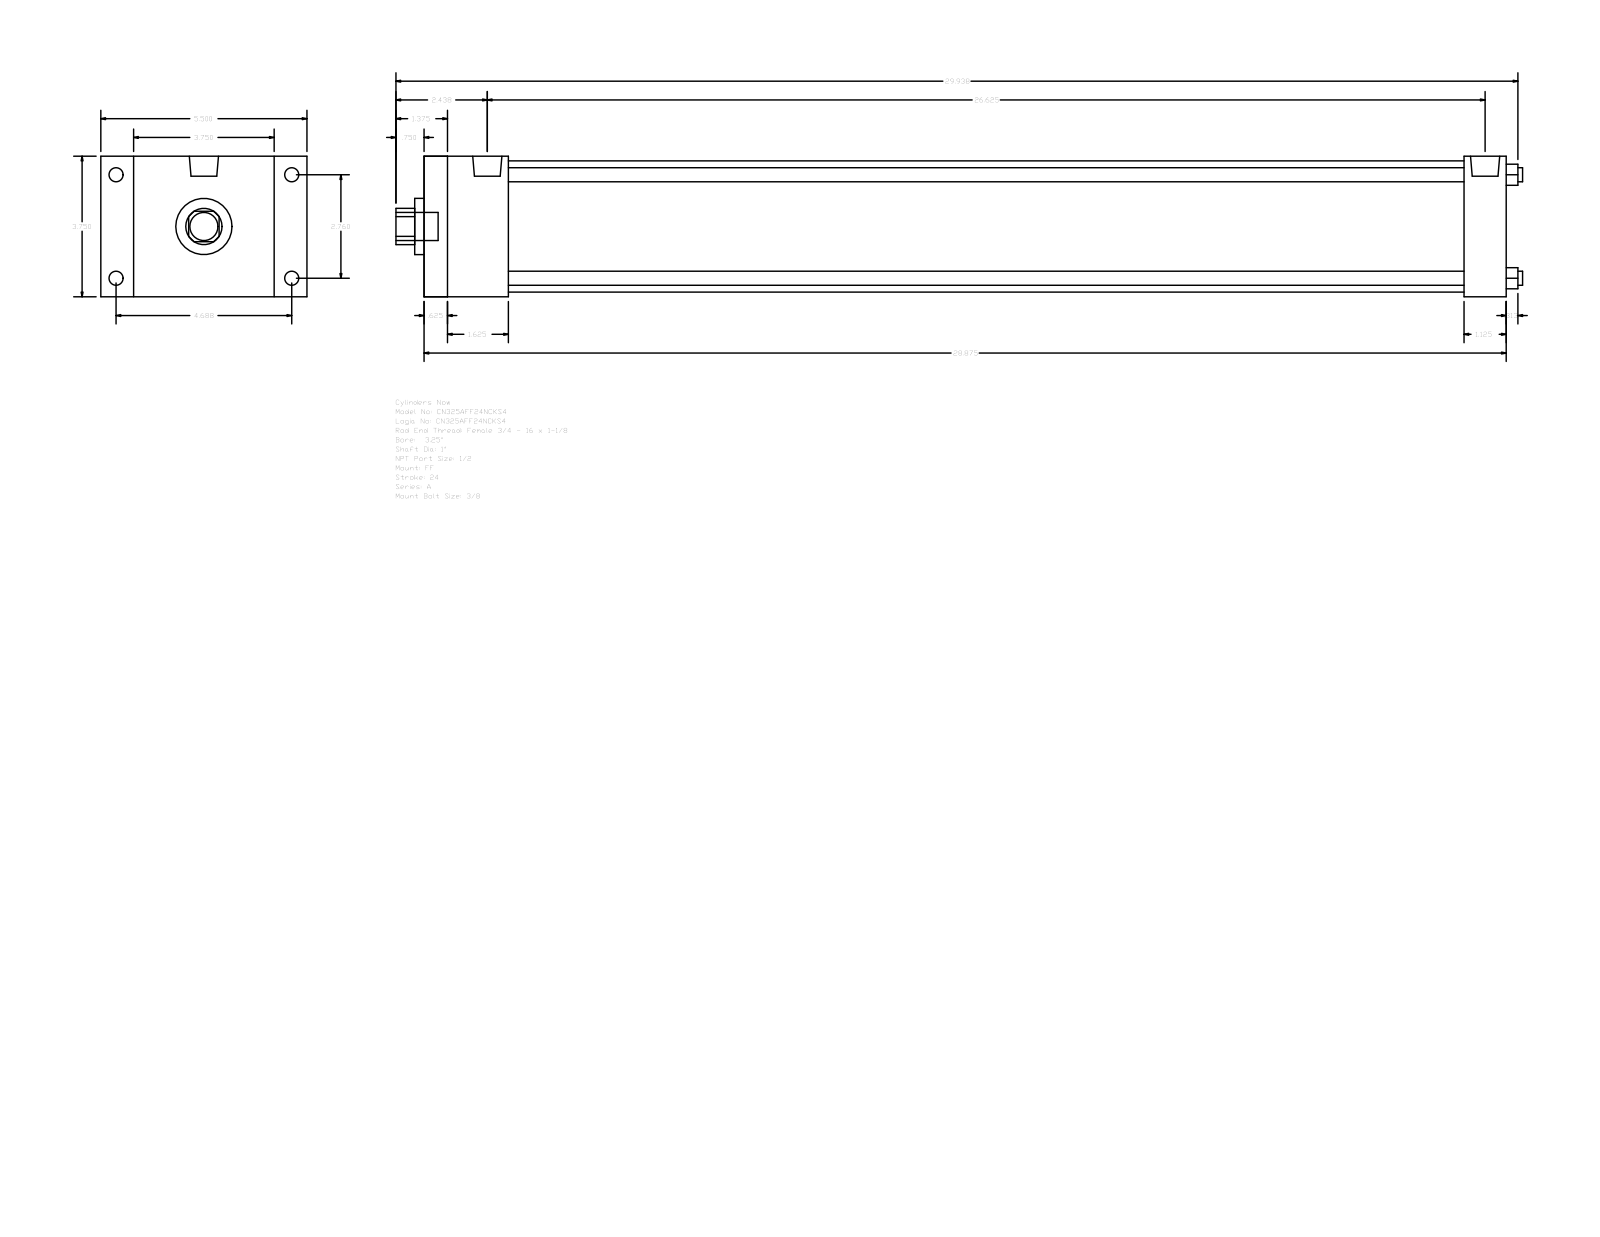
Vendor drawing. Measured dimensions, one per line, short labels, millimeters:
name: A_FF__0325_1
written by: GSSL Pune (CONFIG_CONTROL_DESIGN)
unit: mm
bodies: 0 solids, 92 faces (64 planar, 28 cylindrical, 0 other)
size: 763.59 × 139.7 × 95.25
holes: 4× ⌀9.53, 1× ⌀25.4, 1× ⌀38.1, 1× ⌀88.9
bosses: 4× ⌀9.53, 4× ⌀8.73, 2× ⌀19.77, 1× ⌀19.05
rounds: 1× R12.29
face distances: 95.24, 733.43, 15.87, 717.56, 22.23, 117.47, 57.15, 704.85, 41.28, 688.98
hole spacings: 49.57, 70.1, 99.14
